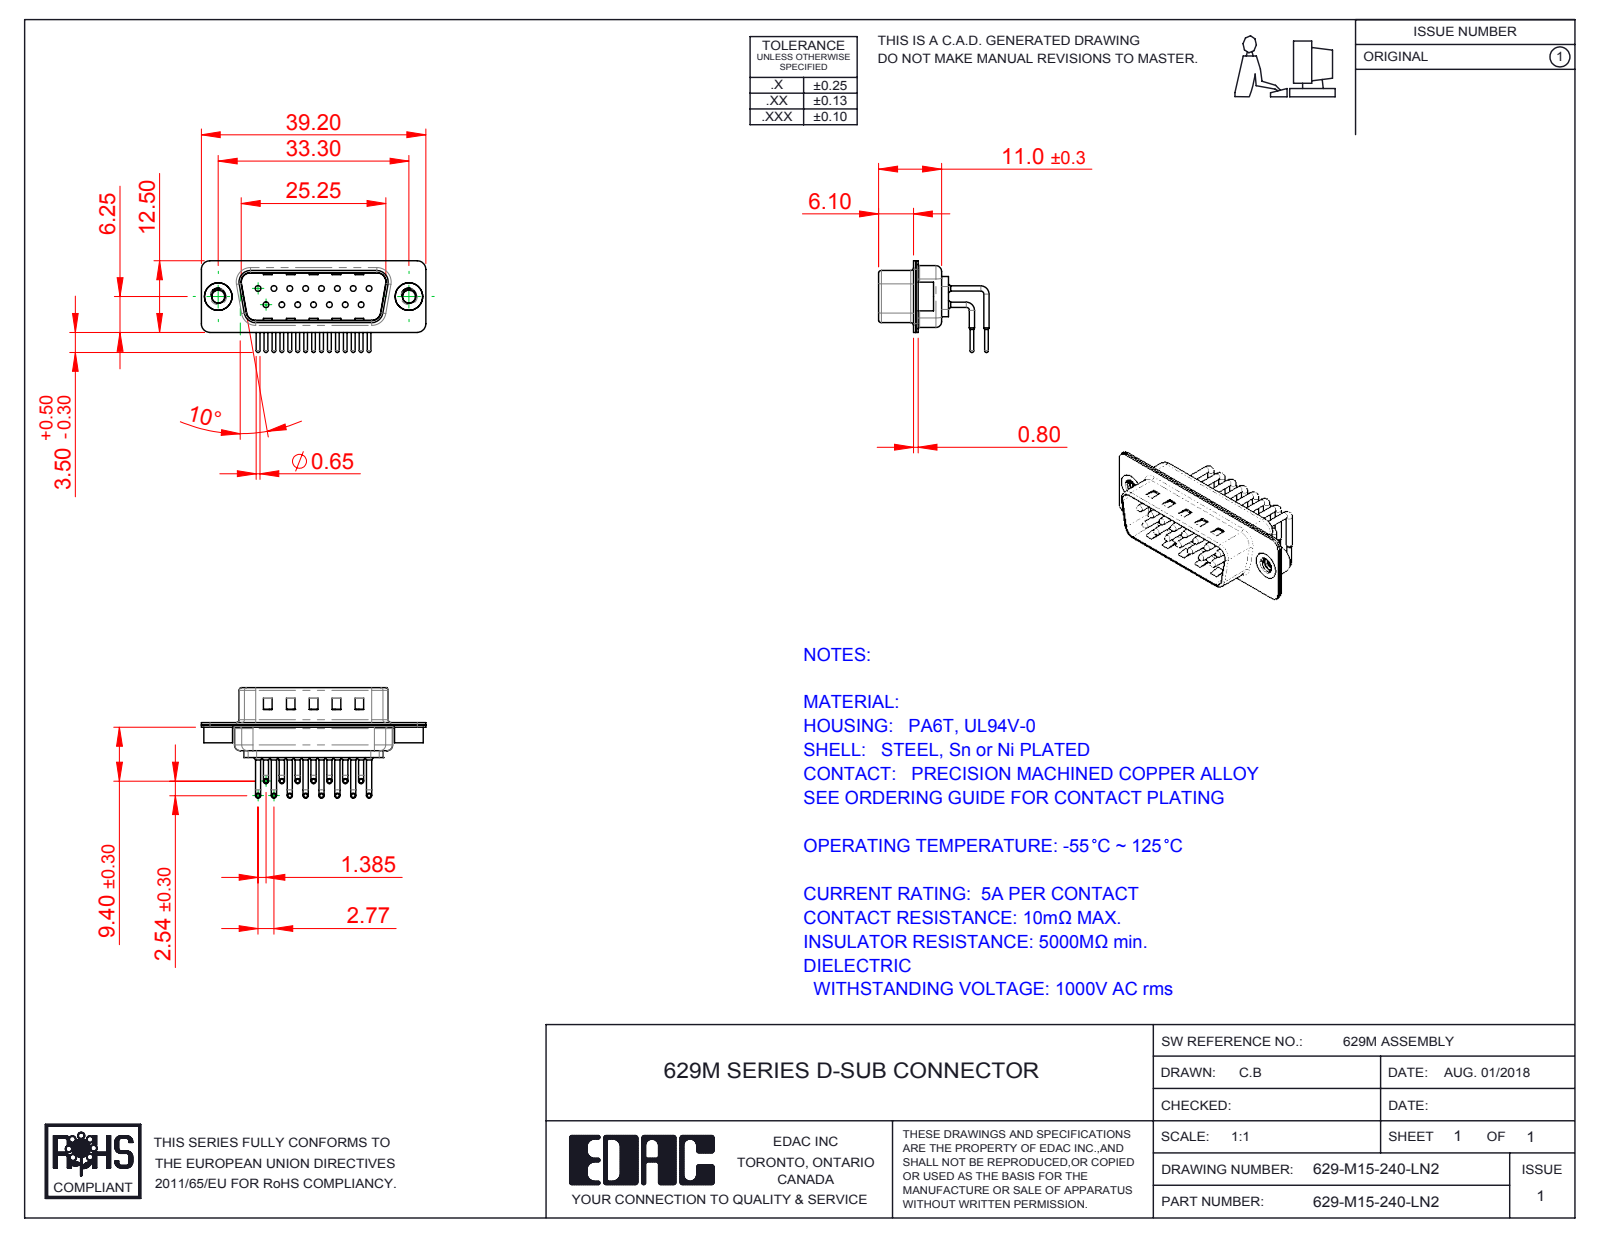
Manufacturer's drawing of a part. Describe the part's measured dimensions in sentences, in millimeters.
The part is named "629M Housing_15 Contacts; 629M Shell Rear_15 Contacts; 629M Shell Front_15 Contacts; 629M Contact Row 1 (+3 more)". Its 3-D file was written by "SolidWorks 2016 (CONFIG_CONTROL_DESIGN)". It is 20 solids with 1990 faces: 1099 planar, 673 cylindrical and 218 other. Overall it measures 39.2 by 19.29 by 16 millimeters. Its volume is 1 960 cubic millimeters and its surface area 5 364 square millimeters. Round holes: 15 of diameter 1, 15 of diameter 1.7, 15 of diameter 2, 2 of diameter 2.26, 2 of diameter 4, 2 of diameter 4.8. Round bosses or shafts: 30 of diameter 0.9, 15 of diameter 1.5, 15 of diameter 0.65, 2 of diameter 5, 2 of diameter 4.9. Partial cylindrical surfaces (rounded edges, fillets, slot ends): 16 of radius 1.5, 15 of radius 1.01, 12 of radius 2, 8 of radius 0.5, 8 of radius 1.6, 4 of radius 0.25, 4 of radius 0.6, 4 of radius 0.65. The main face-to-face distances are 0.4, 0.85, 9.55, 8.7, 1.25, 10.4, 0.8, 1.5, 0.35, 1.9. The hole center spacings are 3.16, 2.77, 5.54, 8.31, 11.08, 5.03, 5.04, 7.48.
